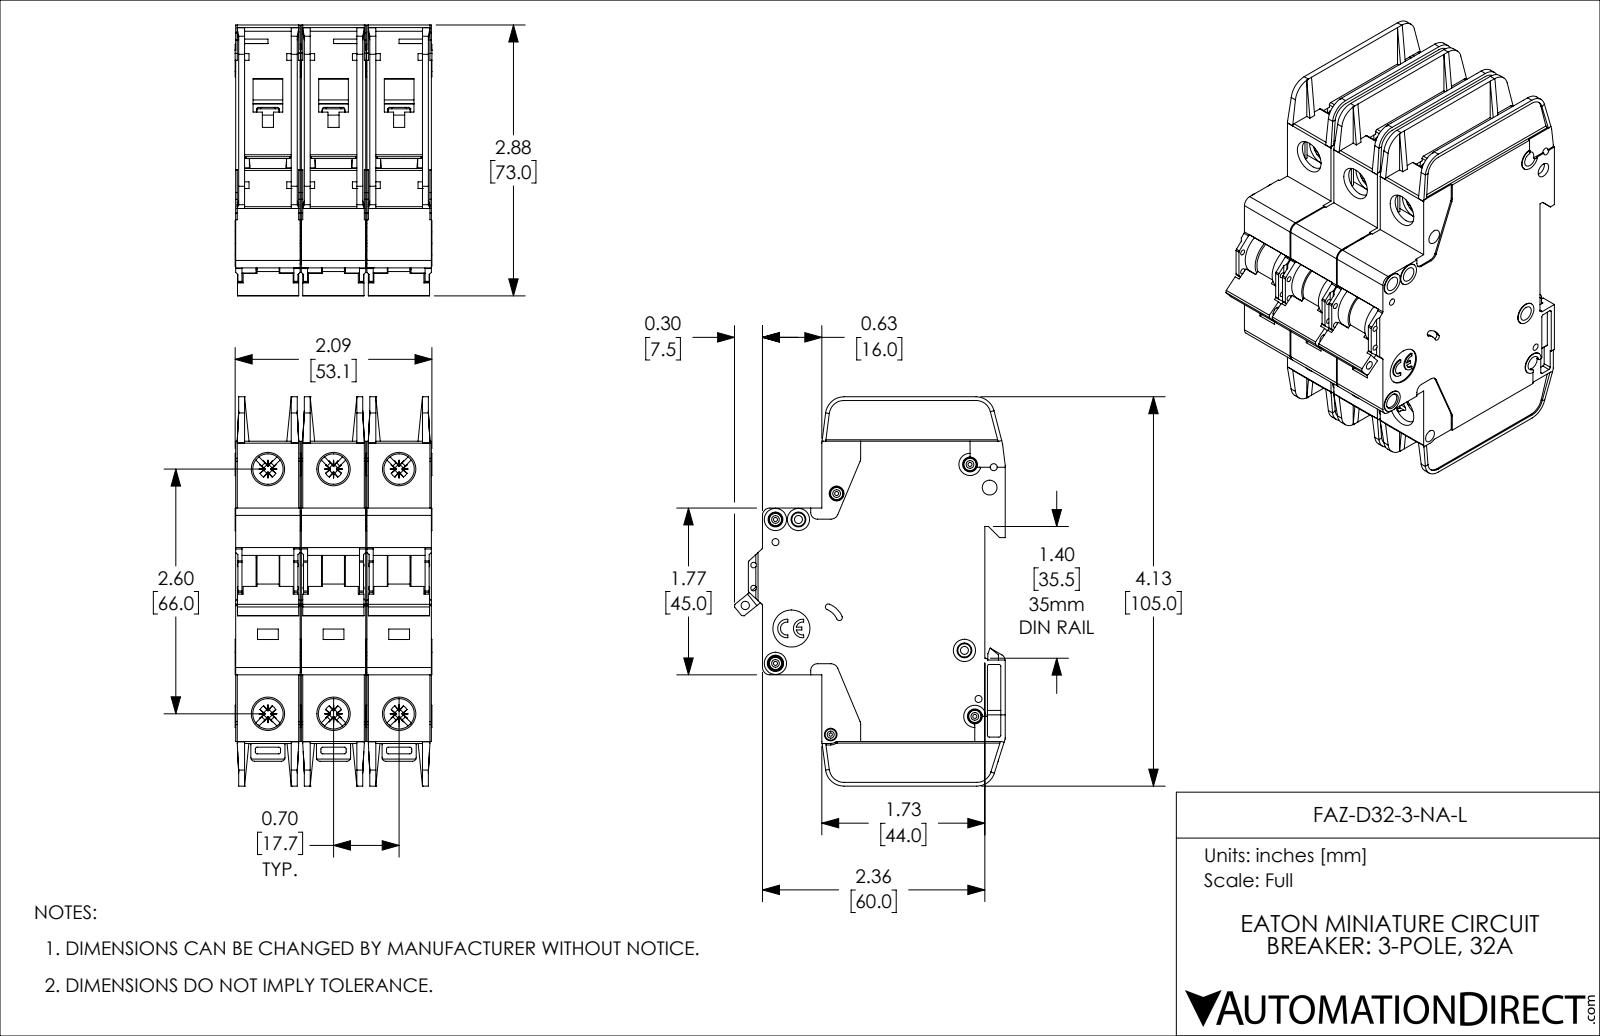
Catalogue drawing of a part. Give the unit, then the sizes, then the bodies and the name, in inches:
Units: inches
Overall size (bounding box): 4.134 × 2.876 × 2.091
Round holes (diameter × count): ⌀0.157 ×8, ⌀0.323 ×6, ⌀0.043 ×5, ⌀0.075 ×4, ⌀0.059 ×2, ⌀0.085 ×2, ⌀0.035 ×1, ⌀0.089 ×1, ⌀0.098 ×1, ⌀0.134 ×1, ⌀0.394 ×1
Round bosses / shafts (diameter × count): ⌀0.13 ×5, ⌀0.236 ×4, ⌀0.118 ×4, ⌀0.098 ×3
Partial cylindrical surfaces — rounded edges, fillets, slot ends (radius × count): R0.02 ×72, R0.016 ×30, R0.039 ×18, R0.043 ×12, R0.079 ×12, R0.008 ×6, R0.01 ×6, R0.028 ×6
Main face-to-face distances: 0.697, 0.047, 1.394, 0.685, 0.591, 1.382, 0.744, 0.65, 0.106, 0.094
Hole centre spacings: 0.697, 2.69, 2.598, 0.244, 0.537, 0.87, 1.394, 2.948
Volume: 14.05 in³ · Surface area: 123 in²
Bodies: 3 solids, 3381 faces (2013 planar, 1071 cylindrical, 297 other)
Part name (STEP PRODUCT): FAZ-D32-3-NA-L
STEP written by: SolidWorks 2019 (AUTOMOTIVE_DESIGN)
